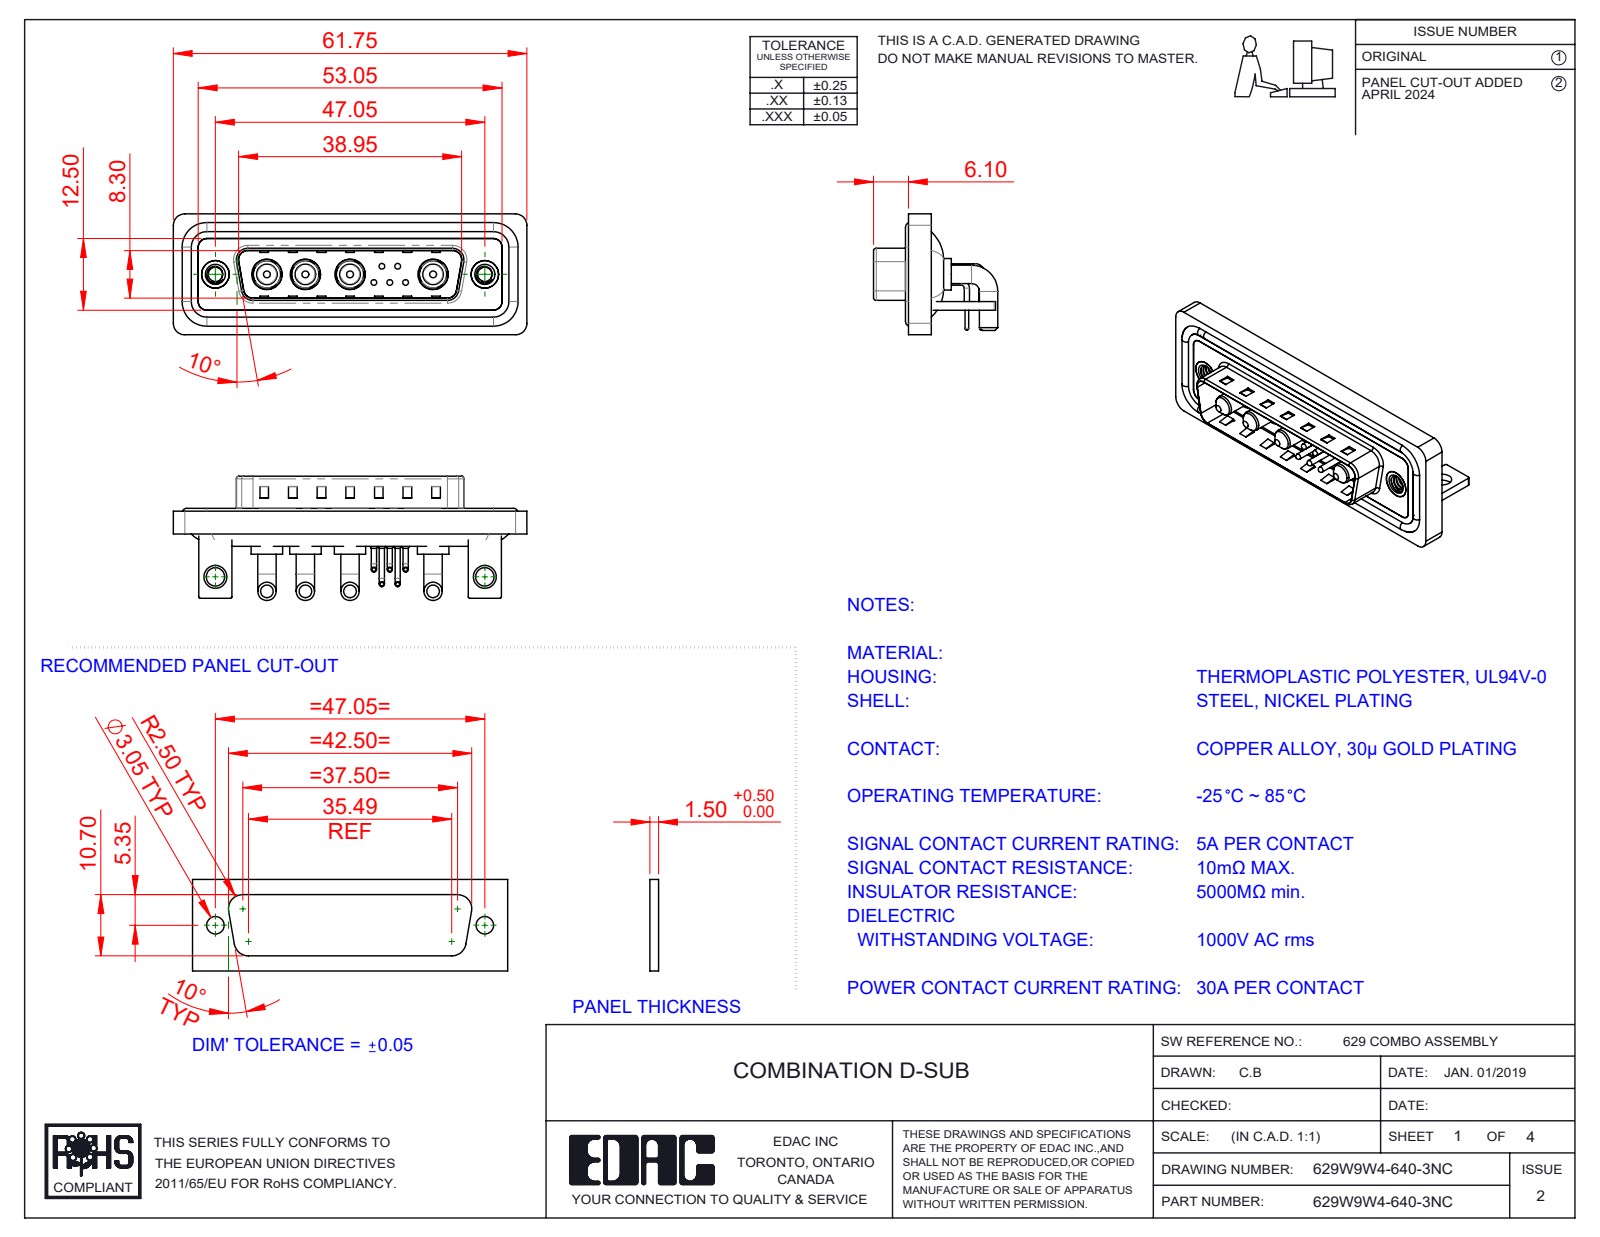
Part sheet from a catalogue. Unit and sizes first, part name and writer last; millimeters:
Units: millimetres
Overall size (bounding box): 61.75 × 21.7 × 21.1
Round holes (diameter × count): ⌀0.75 ×5, ⌀1.6 ×5, ⌀2 ×5, ⌀4.85 ×4, ⌀5.3 ×4, ⌀2.5 ×2, ⌀3.2 ×2, ⌀4 ×2, ⌀4.8 ×2, ⌀5 ×2
Round bosses / shafts (diameter × count): ⌀0.9 ×10, ⌀3.2 ×8, ⌀1.5 ×5, ⌀1 ×5, ⌀0.65 ×5, ⌀5.5 ×4, ⌀5.2 ×4, ⌀4.75 ×4
Partial cylindrical surfaces — rounded edges, fillets, slot ends (radius × count): R2 ×19, R1.5 ×18, R0.25 ×16, R0.5 ×9, R1.6 ×8, R1.01 ×5, R0.6 ×4, R0.65 ×4
Main face-to-face distances: 0.4, 1.5, 0.8, 2.9, 2.1, 1.1, 3.7, 4.1, 4.5, 1.6
Hole centre spacings: 3.16, 2.77, 5.04, 14.5, 47.05, 2.78, 4.4, 4.41
Volume: 8 089 mm³ · Surface area: 13 038 mm²
Bodies: 22 solids, 1243 faces (589 planar, 470 cylindrical, 184 other)
Part name (STEP PRODUCT): 629Combo Housing_9W4; Power Pin_30A RA; 629Combo Waterproof Housing_25 Contacts; 629Combo Stabilizer Bracket (+6 more)
STEP written by: SolidWorks 2023 (CONFIG_CONTROL_DESIGN)
